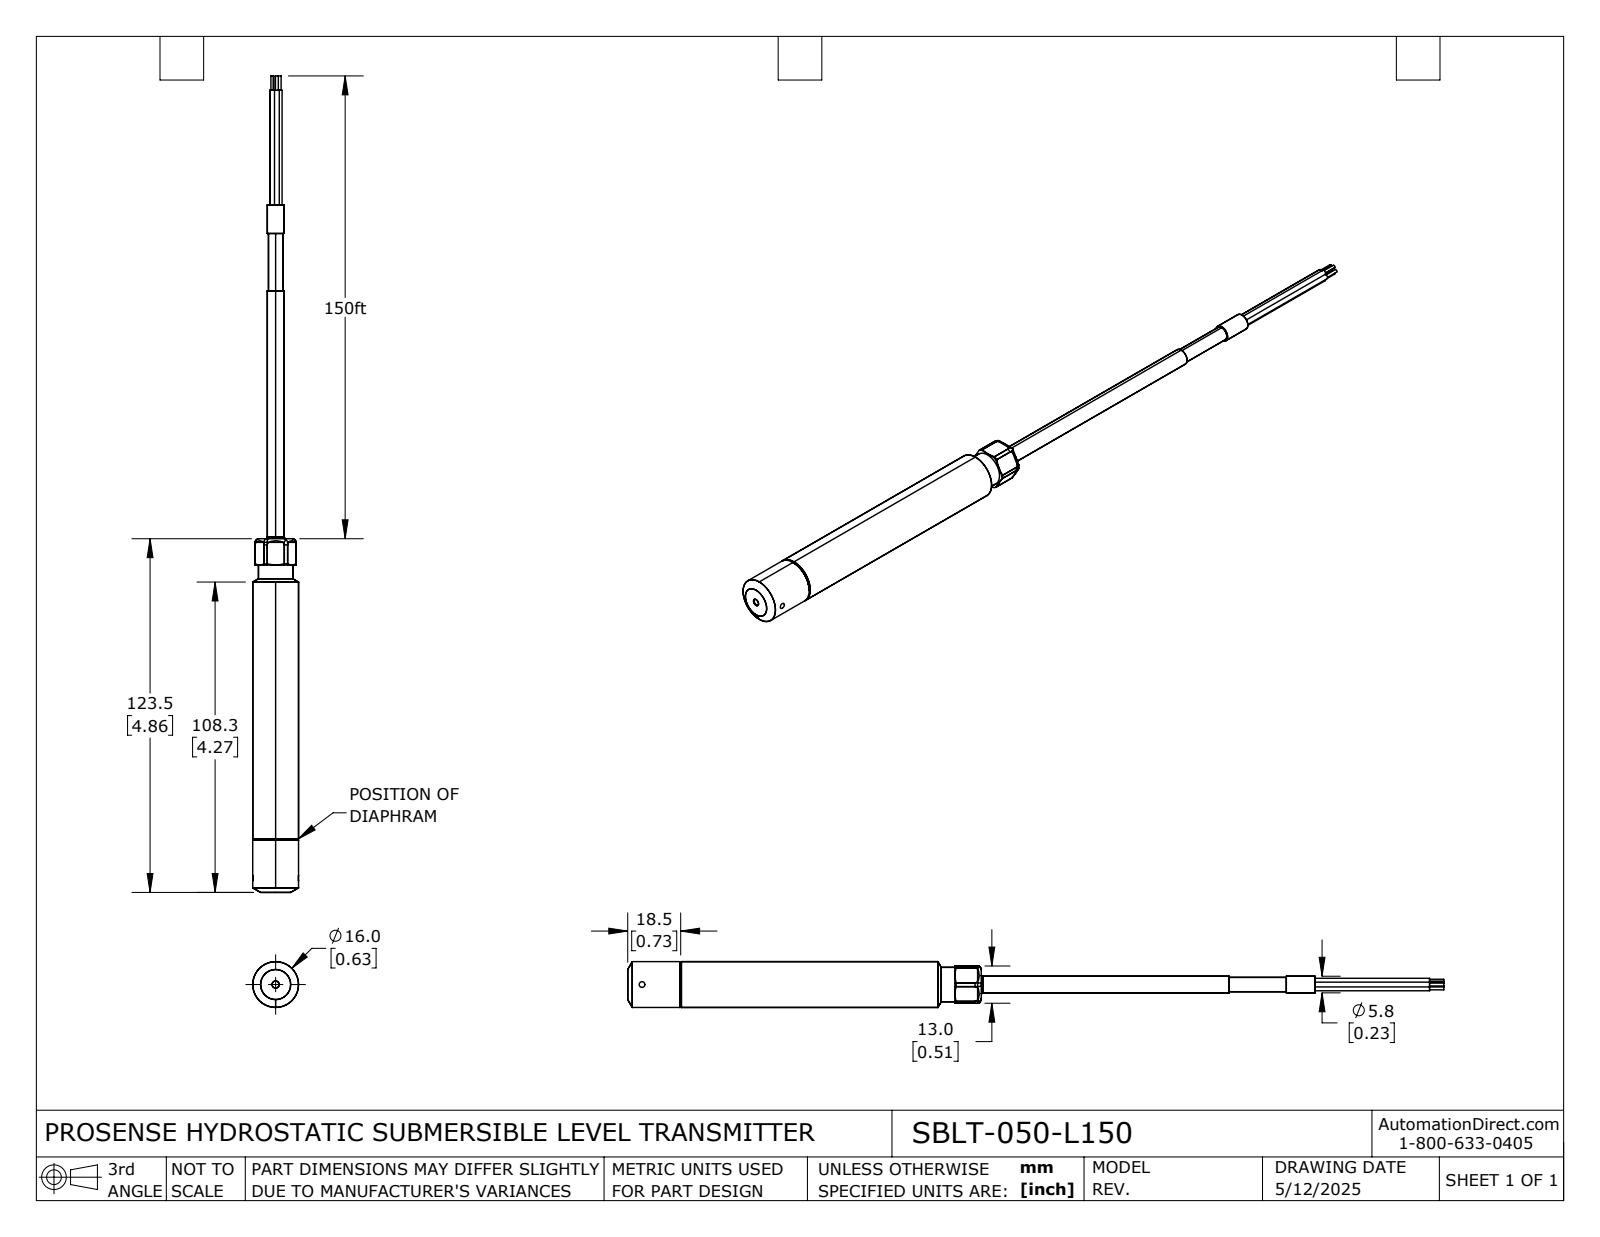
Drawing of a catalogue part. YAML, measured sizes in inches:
part_name: "SBLT-050-L150"
step_written_by: "SolidWorks 2024 (AUTOMOTIVE_DESIGN)"
units: inches
bodies: {solids: 11, faces: 201, planar: 52, cylindrical: 88, other: 61}
overall_size: [11.221, 0.63, 0.63]
volume: 3.198
surface_area: 29.94
round_holes:
  - {diameter: 0.079, count: 1}
  - {diameter: 0.098, count: 1}
  - {diameter: 0.374, count: 1}
  - {diameter: 0.516, count: 1}
  - {diameter: 0.551, count: 1}
round_bosses_or_shafts:
  - {diameter: 0.066, count: 5}
  - {diameter: 0.039, count: 5}
  - {diameter: 0.63, count: 1}
  - {diameter: 0.629, count: 1}
  - {diameter: 0.472, count: 1}
  - {diameter: 0.472, count: 1}
  - {diameter: 0.244, count: 1}
  - {diameter: 0.228, count: 1}
partial_cylinders:
  - {radius: 0.05, count: 6}
  - {radius: 0.281, count: 1}
face_to_face_distances: [0.512, 4.861, 4.33, 0.531, 4.589, 8.918, 9.45, 3.77, 0.197, 8.721]
